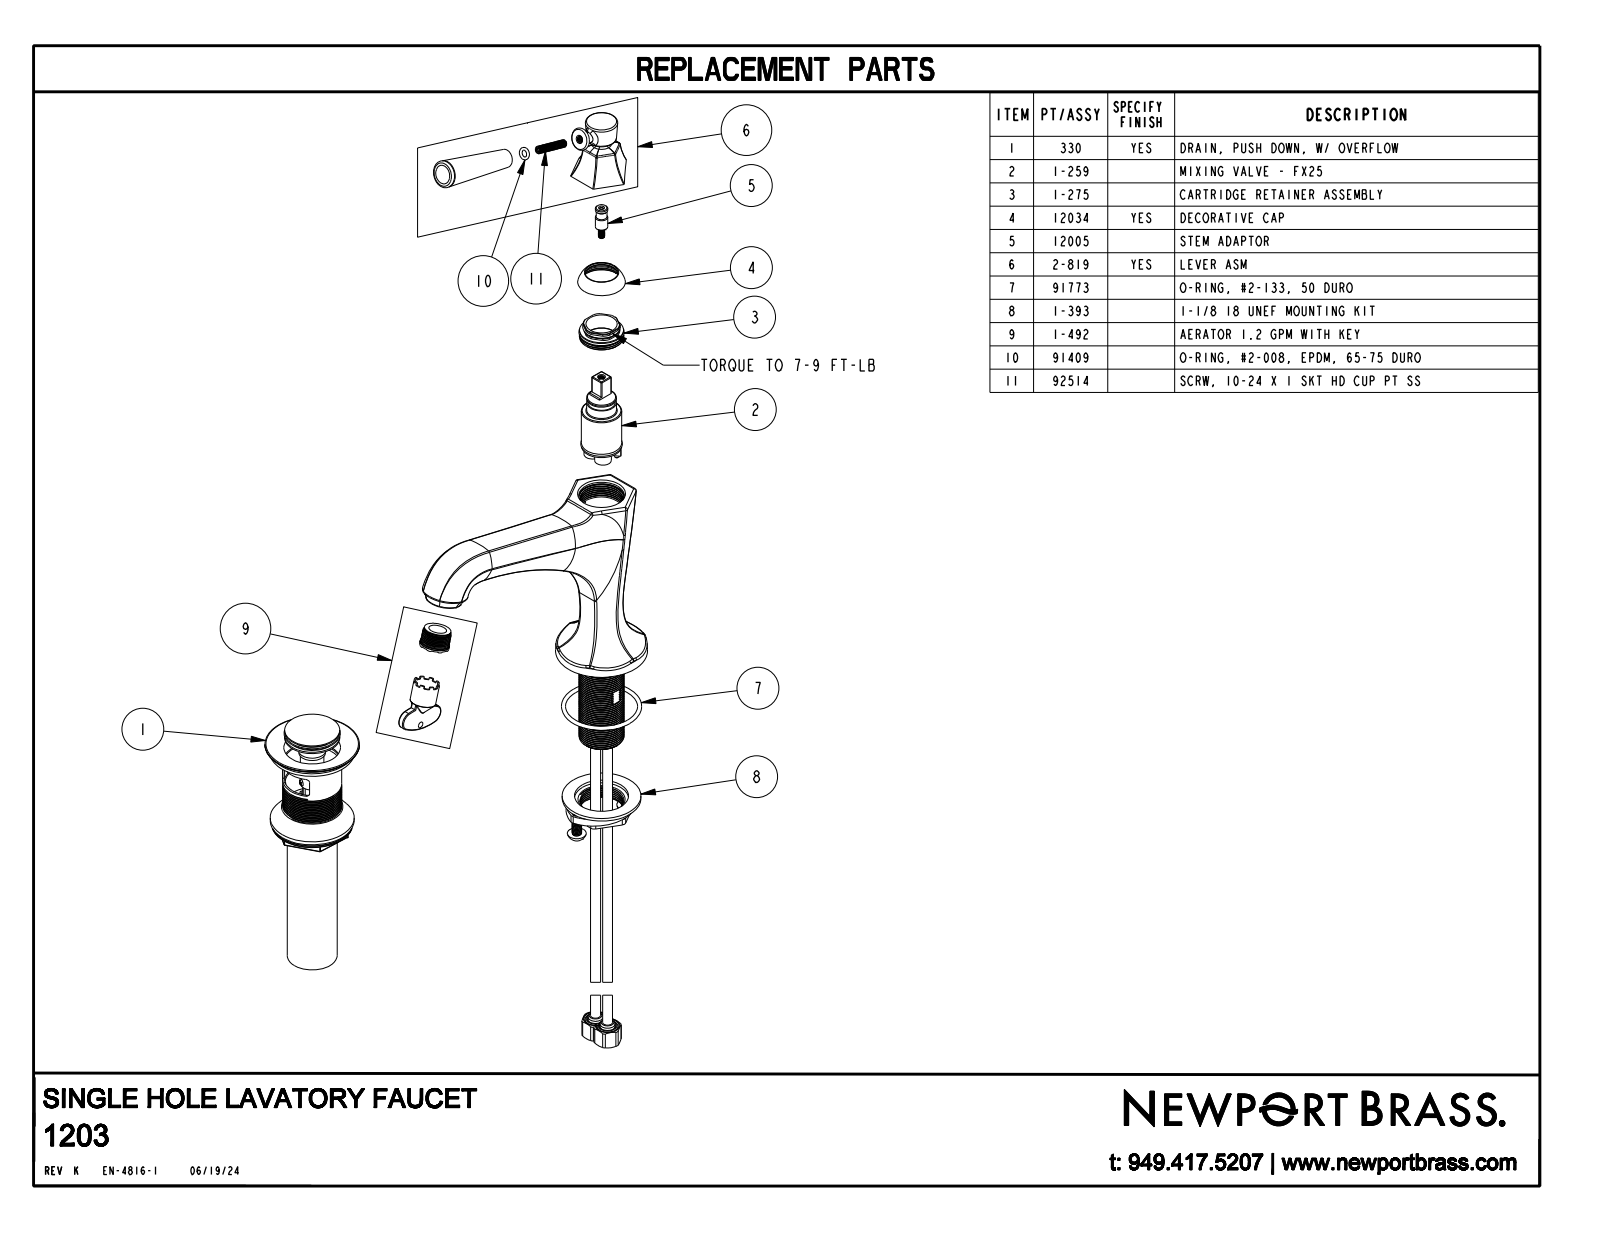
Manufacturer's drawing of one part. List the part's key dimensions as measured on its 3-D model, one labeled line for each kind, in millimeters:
Part name (STEP PRODUCT): 1203
STEP written by: CREO PARAMETRIC BY PTC INC, 2018400 (AUTOMOTIVE_DESIGN)
Units: millimetres
Bodies: 2 solids, 259 faces (17 planar, 13 cylindrical, 229 other)
Overall size (bounding box): 183.8 × 182.2 × 58.4
Volume: 244 800 mm³ · Surface area: 41 990 mm²
Round holes (diameter × count): ⌀20.6 ×1, ⌀25.1 ×1, ⌀28.8 ×1
Partial cylindrical surfaces — rounded edges, fillets, slot ends (radius × count): R1.5 ×5
Main face-to-face distances: 119.6, 122.1, 2.5, 128.2, 8.6, 6, 128.3, 8.7, 6.1, 123.7
